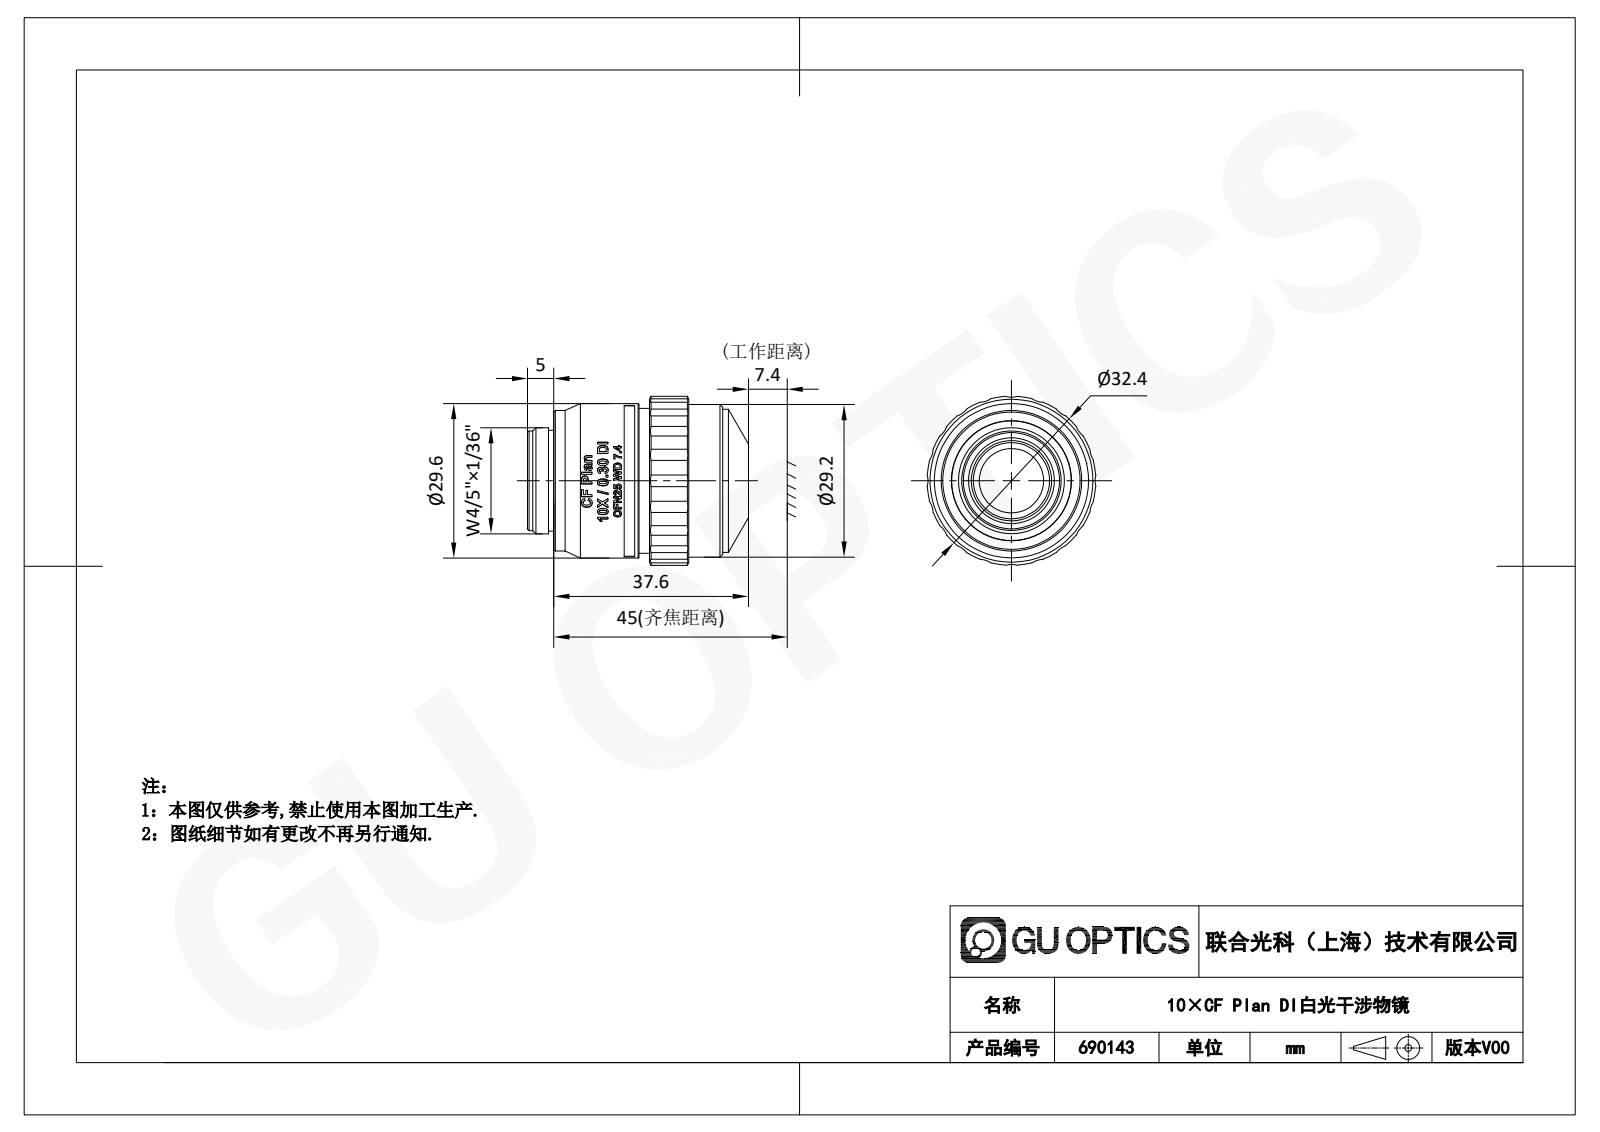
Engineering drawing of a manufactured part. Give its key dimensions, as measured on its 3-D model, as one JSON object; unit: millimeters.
{"part_name": "690143", "step_written_by": "SolidWorks 2020 (CONFIG_CONTROL_DESIGN)", "units": "millimeters", "bodies": {"solids": 7, "faces": 519, "planar": 168, "cylindrical": 128, "other": 223}, "overall_size": [42.3, 32.32, 32.32], "volume_mm3": 14743, "surface_area_mm2": 18926, "round_holes": [[7.6, 1], [8.4, 1], [11, 1], [12, 1], [12.4, 1], [13.4, 1], [14.5, 1], [15.4, 1], [15.5, 1], [20, 1], [20.5, 1], [20.7, 1]], "round_bosses_or_shafts": [[30, 1], [29.6, 1], [29.2, 1], [27.7, 1], [27.4, 1], [27, 1], [26.9, 1], [26.3, 1]], "partial_cylinders_radius": [[4, 20], [14.7, 1], [16.2, 1]], "face_to_face_distances": [8.5, 1.5, 31.9, 2.9, 34.8, 7.55, 13.35, 11.35, 8.45, 23.45]}
